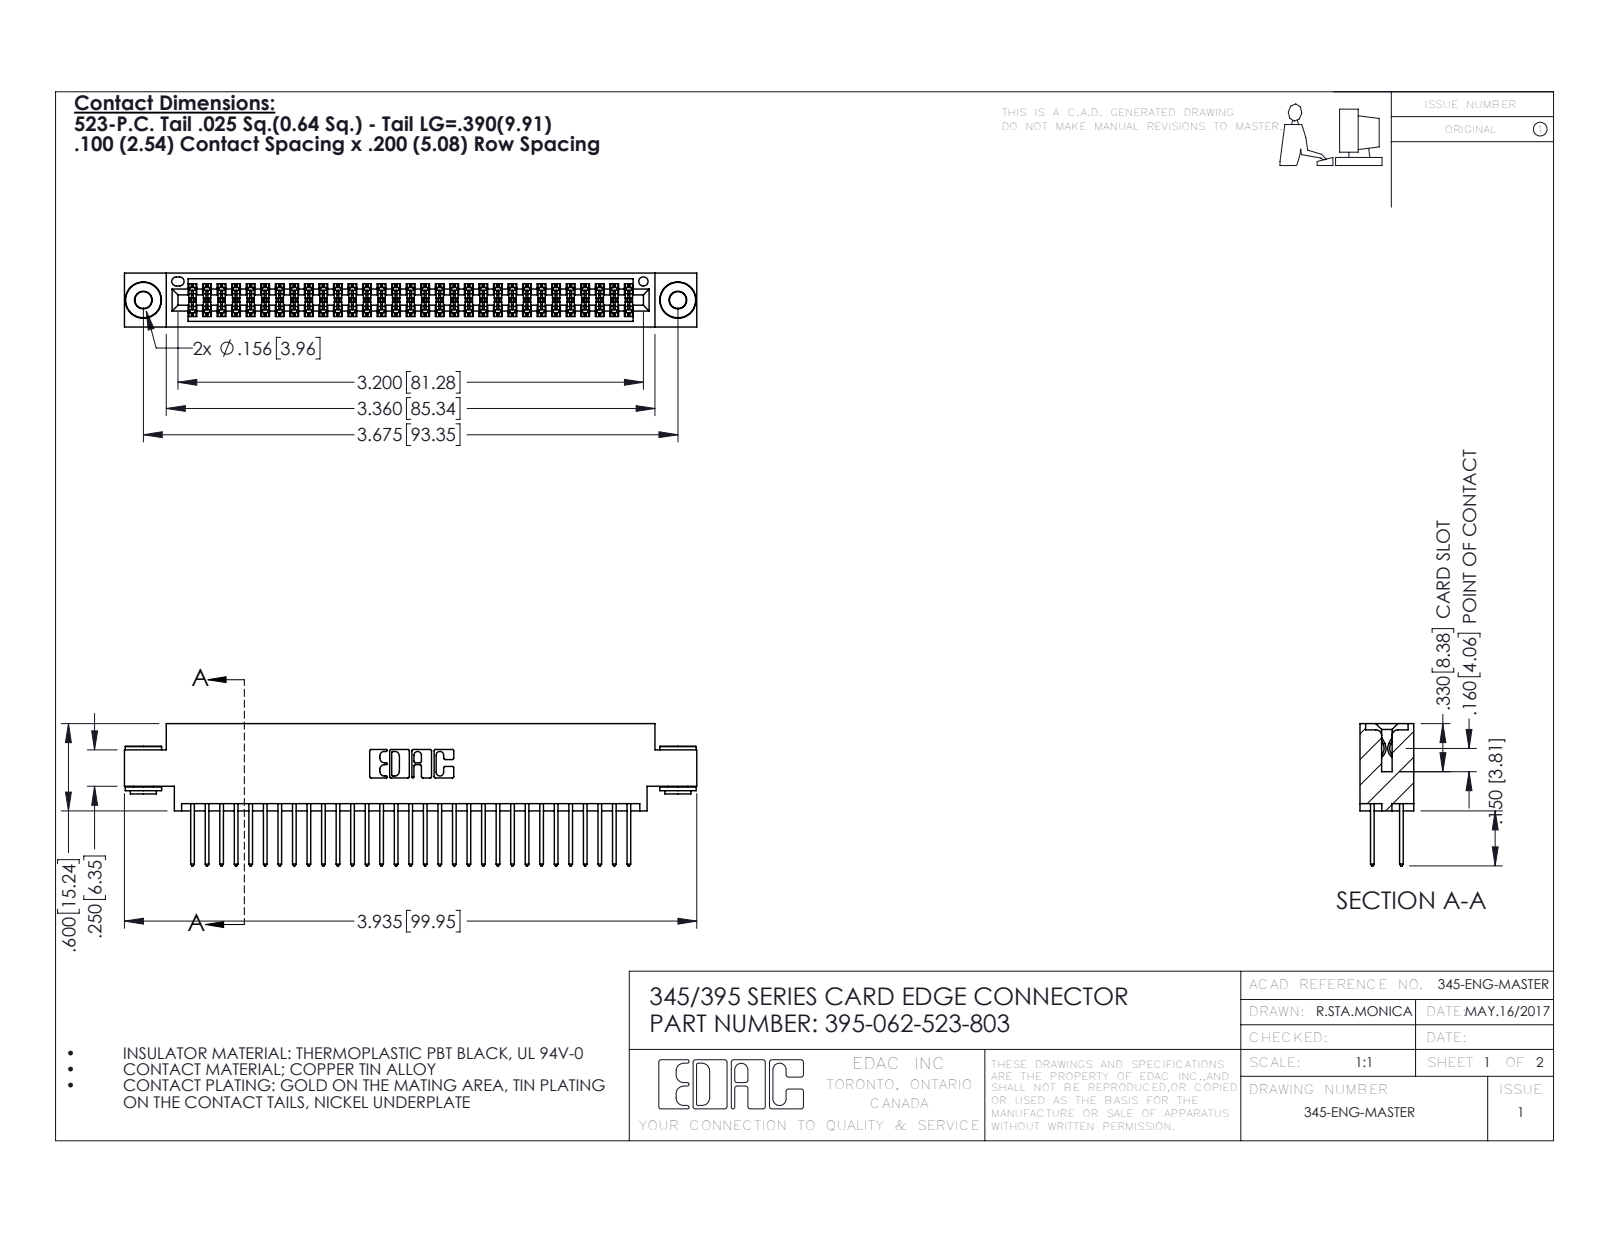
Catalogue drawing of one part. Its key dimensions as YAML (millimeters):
part_name: "395-062-523-803; 345-250-002_345-250-002-102; 345-292-001_345-293-123; 345 Part_0.170 Offset - 0.156 Dia-TH"
step_written_by: "SolidWorks 2016 (CONFIG_CONTROL_DESIGN)"
units: millimeters
bodies: {solids: 65, faces: 3268, planar: 2140, cylindrical: 1120, other: 8}
overall_size: [99.9, 24.8, 9.4]
volume: 9640
surface_area: 14950
round_holes:
  - {diameter: 2.9, count: 2}
  - {diameter: 4, count: 2}
  - {diameter: 1.6, count: 1}
round_bosses_or_shafts:
  - {diameter: 6.4, count: 2}
  - {diameter: 4.6, count: 2}
  - {diameter: 3.5, count: 2}
partial_cylinders:
  - {radius: 0.2, count: 93}
  - {radius: 0.3, count: 62}
  - {radius: 0.3, count: 22}
  - {radius: 0.2, count: 6}
  - {radius: 0.8, count: 6}
  - {radius: 0.7, count: 3}
  - {radius: 0.4, count: 2}
  - {radius: 0.5, count: 2}
face_to_face_distances: [1.8, 7.6, 5.1, 2.5, 6.9, 0.6, 9.4, 5.7, 4.4, 3.8]
hole_center_spacings: [6.9, 87.4, 93.3]
